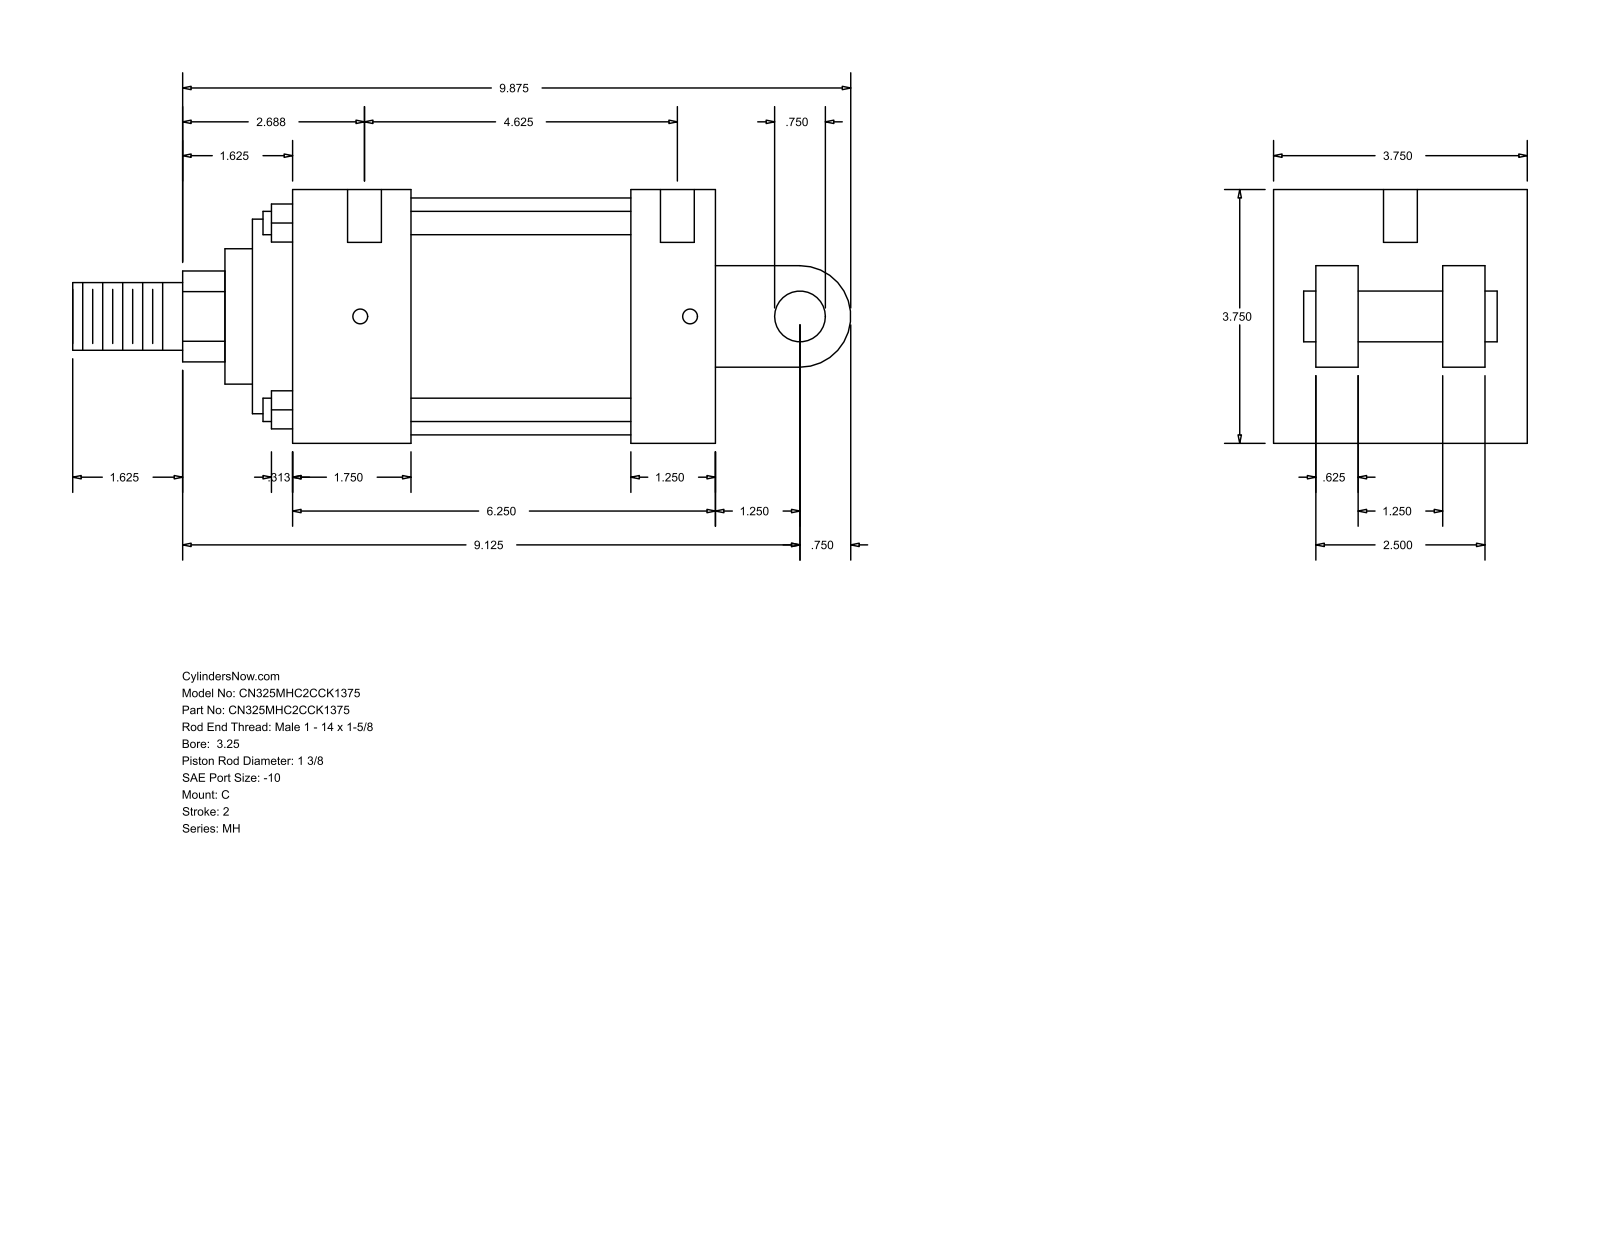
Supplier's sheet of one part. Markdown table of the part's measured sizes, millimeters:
| quantity | value |
| --- | --- |
| part name | MH_C__0325_1.375 |
| STEP written by | GSSL Pune (CONFIG_CONTROL_DESIGN) |
| units | millimeters |
| bodies | 0 solids, 101 faces (71 planar, 30 cylindrical, 0 other) |
| overall size | 292.1 × 95.25 × 95.25 |
| round holes (diameter × count) | 5.56 × 4, 12.7 × 2 |
| round bosses / shafts (diameter × count) | 8.76 × 4, 88.9 × 1, 73.03 × 1, 50.8 × 1, 34.92 × 1, 25.4 × 1, 19.05 × 1 |
| partial cylindrical surfaces (radius × count) | 17.06 × 1, 19.05 × 1 |
| main face-to-face distances | 95.24, 15.87, 63.5, 158.76, 79.37, 31.74, 47.63, 44.45, 127.01, 82.56 |
| hole center spacings | 123.83, 1.59, 4.76, 117.48, 119.07, 122.24 |
